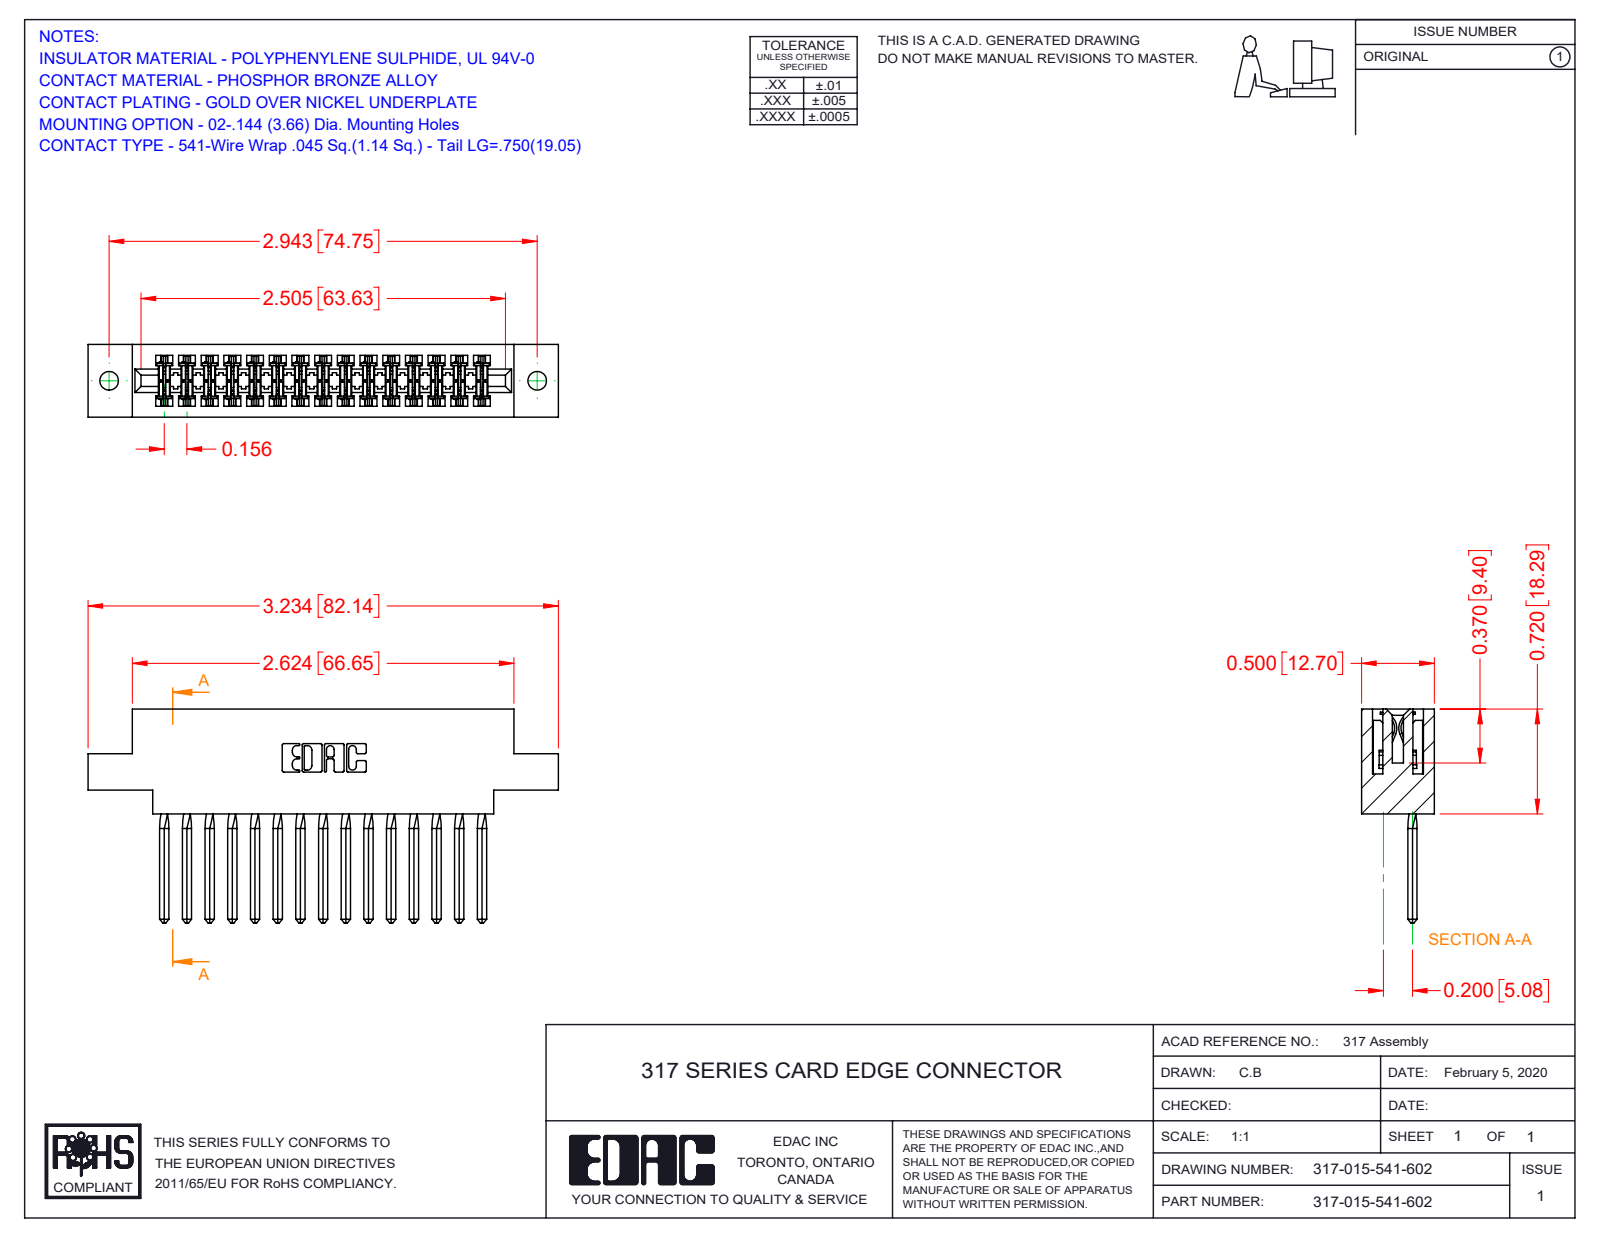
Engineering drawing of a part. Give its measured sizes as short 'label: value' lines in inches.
name: 317 Part_.144 Dia; 317-290-002_541; 317-015-541-602
written by: SolidWorks 2016 (CONFIG_CONTROL_DESIGN)
unit: in
bodies: 16 solids, 2382 faces (1918 planar, 404 cylindrical, 60 other)
size: 3.234 × 1.47 × 0.5
volume: 0.76 in³; area: 25.47 in²
holes: 2× ⌀0.128
rounds: 30× R0.015, 22× R0.01, 6× R0.007, 6× R0.031, 3× R0.026, 2× R0.095, 2× R0.1, 2× R0.11
face distances: 0.5, 0.075, 0.425, 0.11, 0.35, 0.22, 0.195, 0.065, 0.331, 0.72
hole spacings: 2.943
